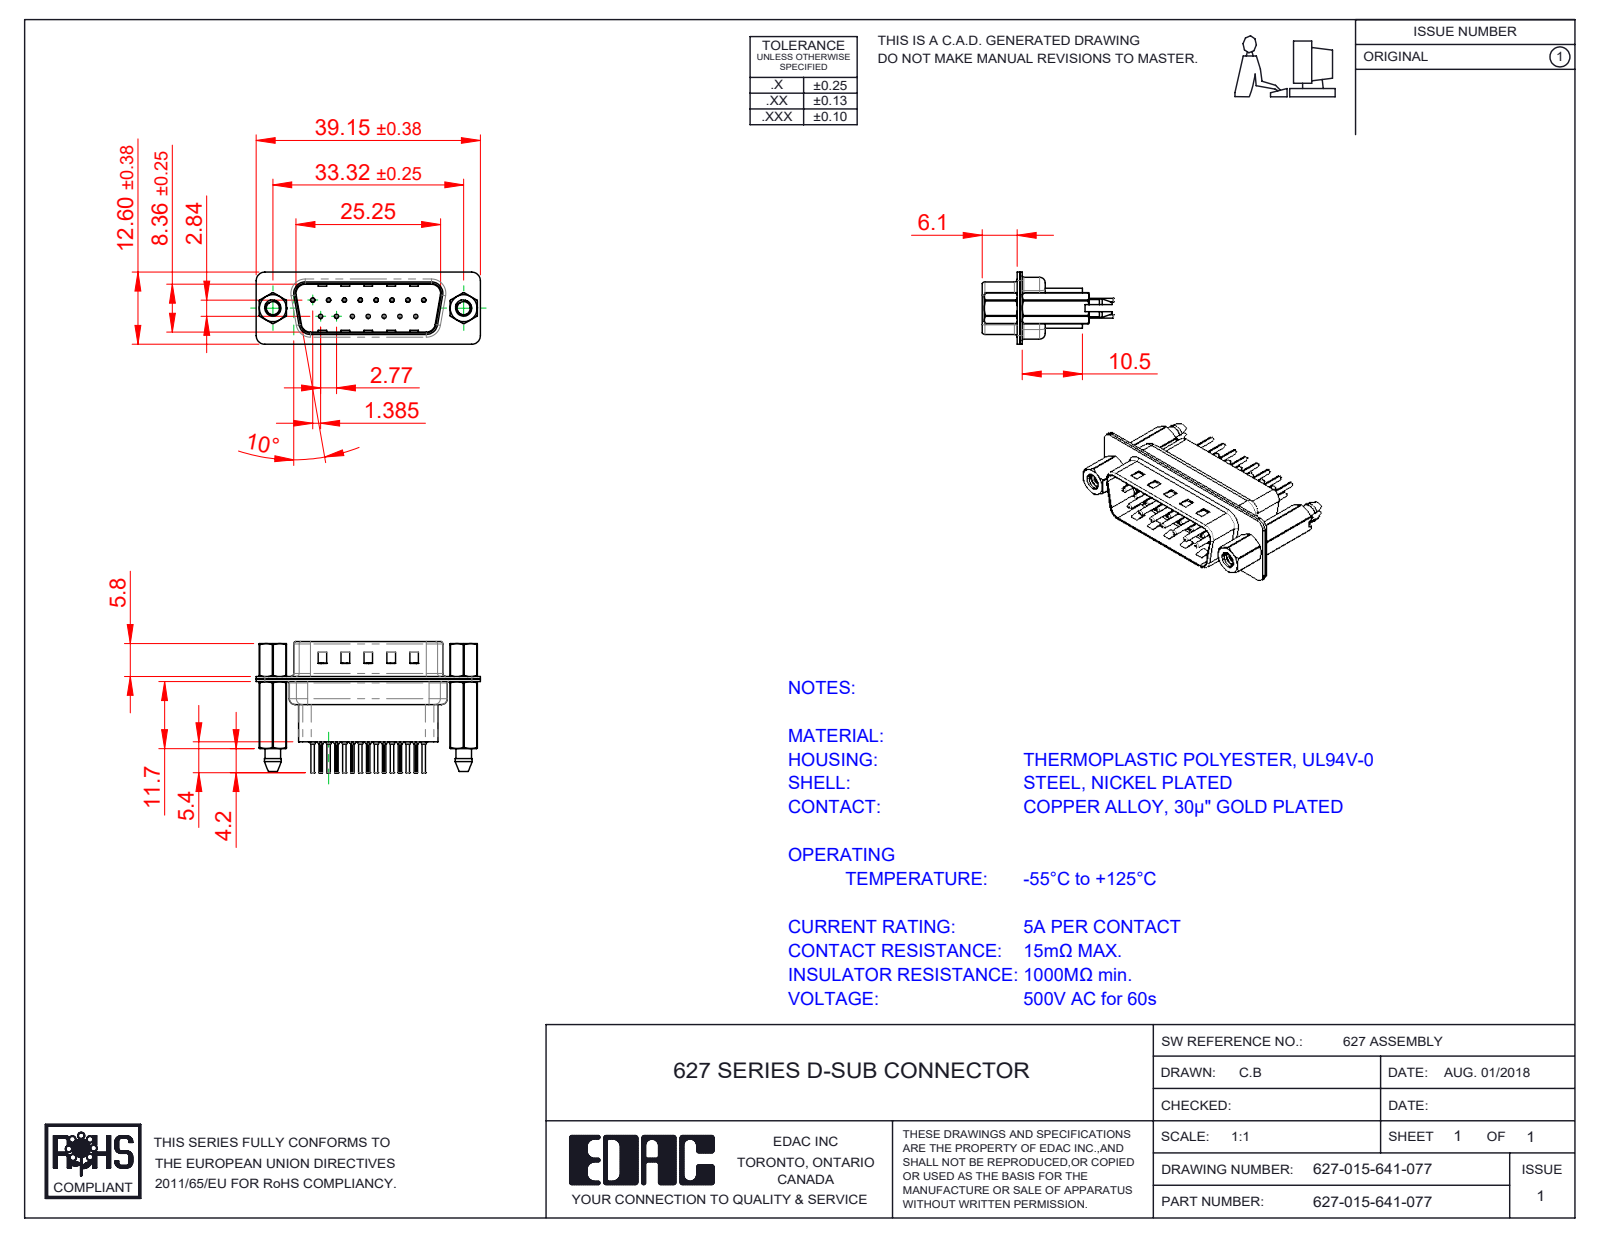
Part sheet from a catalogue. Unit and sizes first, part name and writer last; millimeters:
Units: millimetres
Overall size (bounding box): 39.15 × 22.8 × 12.6
Round holes (diameter × count): ⌀0.2 ×15, ⌀0.35 ×15, ⌀1.1 ×15, ⌀1.6 ×15, ⌀2.26 ×2, ⌀2.29 ×2, ⌀4 ×2, ⌀4.8 ×2
Round bosses / shafts (diameter × count): ⌀2 ×15, ⌀1.5 ×15, ⌀0.75 ×15, ⌀0.6 ×15, ⌀4.9 ×2, ⌀2.79 ×2
Partial cylindrical surfaces — rounded edges, fillets, slot ends (radius × count): R0.1 ×30, R1.5 ×18, R2 ×12, R1.6 ×10, R0.5 ×8, R0.25 ×4, R0.6 ×4, R0.65 ×4
Main face-to-face distances: 0.4, 0.45, 0.9, 4.76, 0.82, 9.58, 1.5, 0.68, 7.68, 1.4
Hole centre spacings: 3.16, 2.77, 5.54, 8.31, 11.08, 5.03, 5.04, 7.48
Volume: 3 039 mm³ · Surface area: 7 805 mm²
Bodies: 22 solids, 2044 faces (553 planar, 826 cylindrical, 665 other)
Part name (STEP PRODUCT): 627 4-40 Hex Standoff; 627 Shell Rear_15 Contacts; 627-015-641-077; 627 4-40 Threaded Boardlock_HP41 (+4 more)
STEP written by: SolidWorks 2020 (CONFIG_CONTROL_DESIGN)
